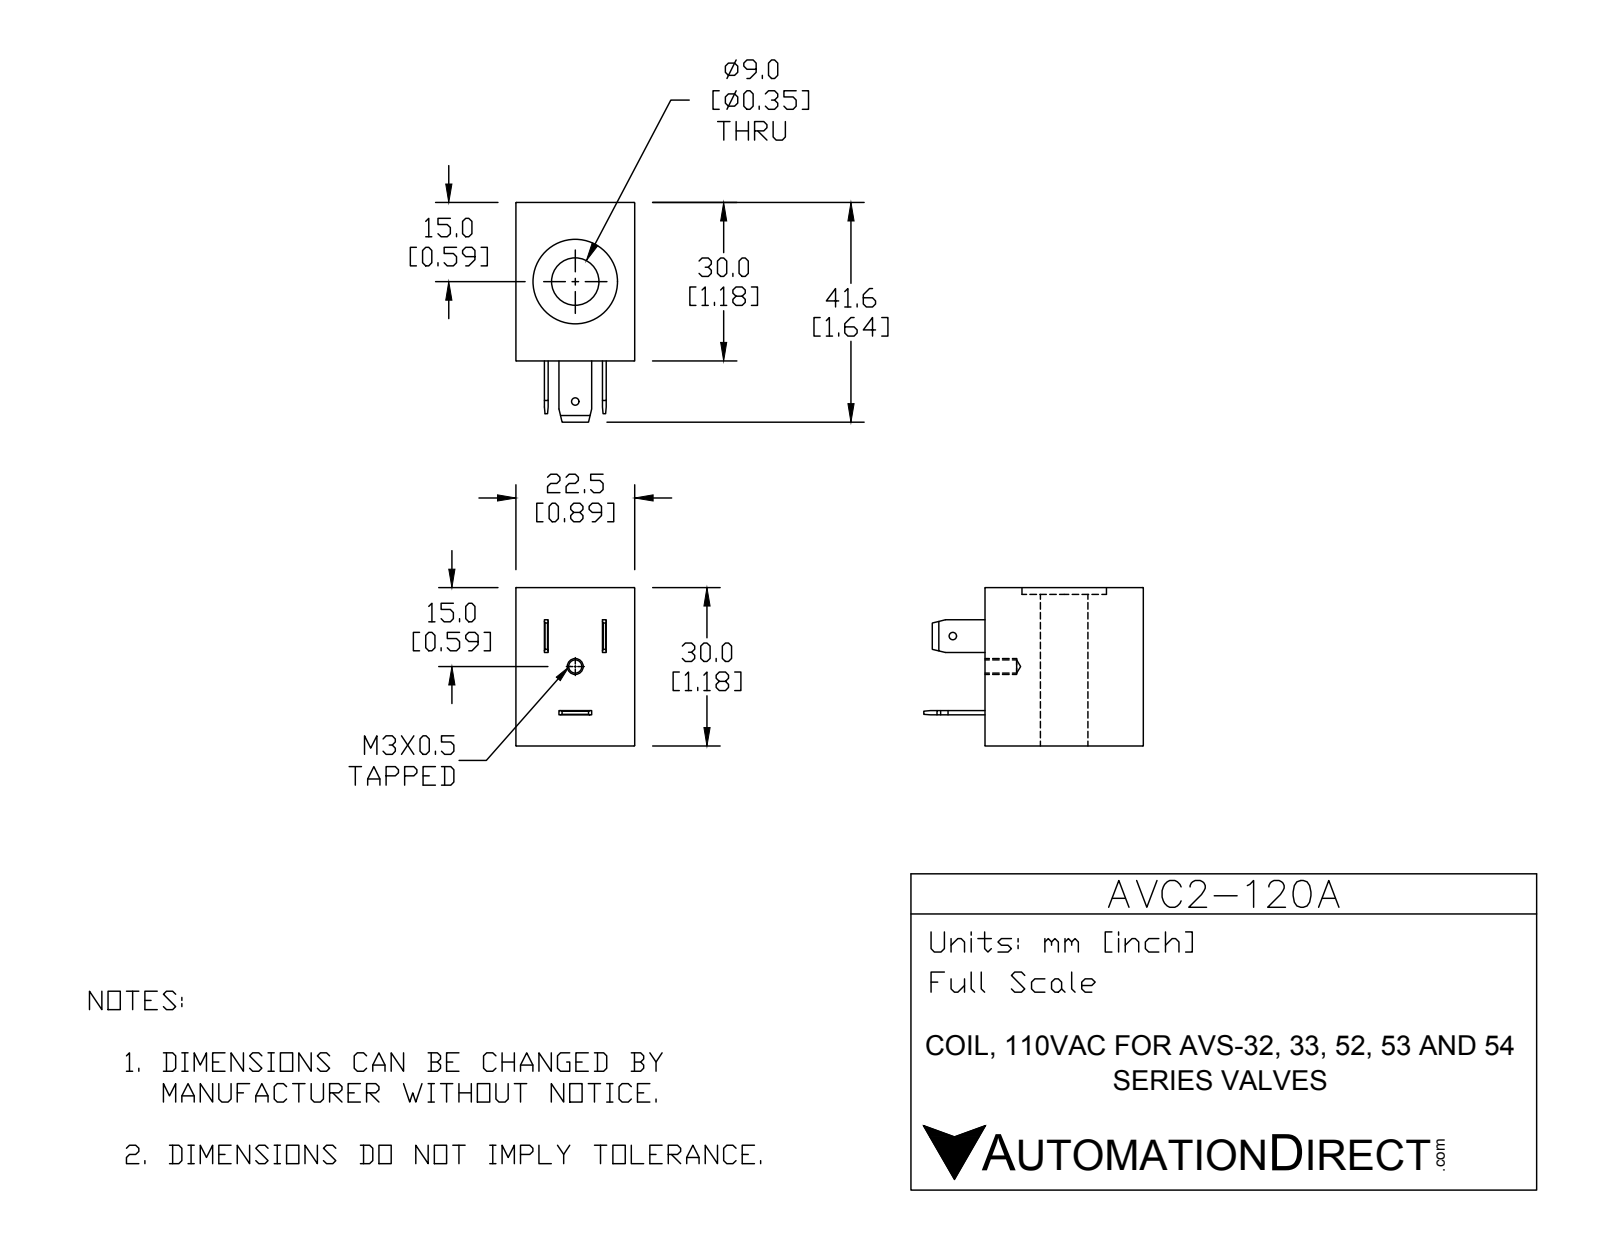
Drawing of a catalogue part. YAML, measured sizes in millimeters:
part_name: "AVC2-120A"
step_written_by: "SolidWorks 2016 (AUTOMOTIVE_DESIGN)"
units: millimeters
bodies: {solids: 1, faces: 60, planar: 34, cylindrical: 20, other: 6}
overall_size: [41.6, 30, 22.5]
volume: 18267
surface_area: 5712
round_holes:
  - {diameter: 1.4, count: 2}
  - {diameter: 2.5, count: 1}
  - {diameter: 9, count: 1}
  - {diameter: 16, count: 1}
partial_cylinders:
  - {radius: 0.1, count: 8}
face_to_face_distances: [30, 22.5, 28.7, 1.3, 11, 6.1, 16.4, 5.4, 17.1, 0.7]
hole_center_spacings: [22.7]
